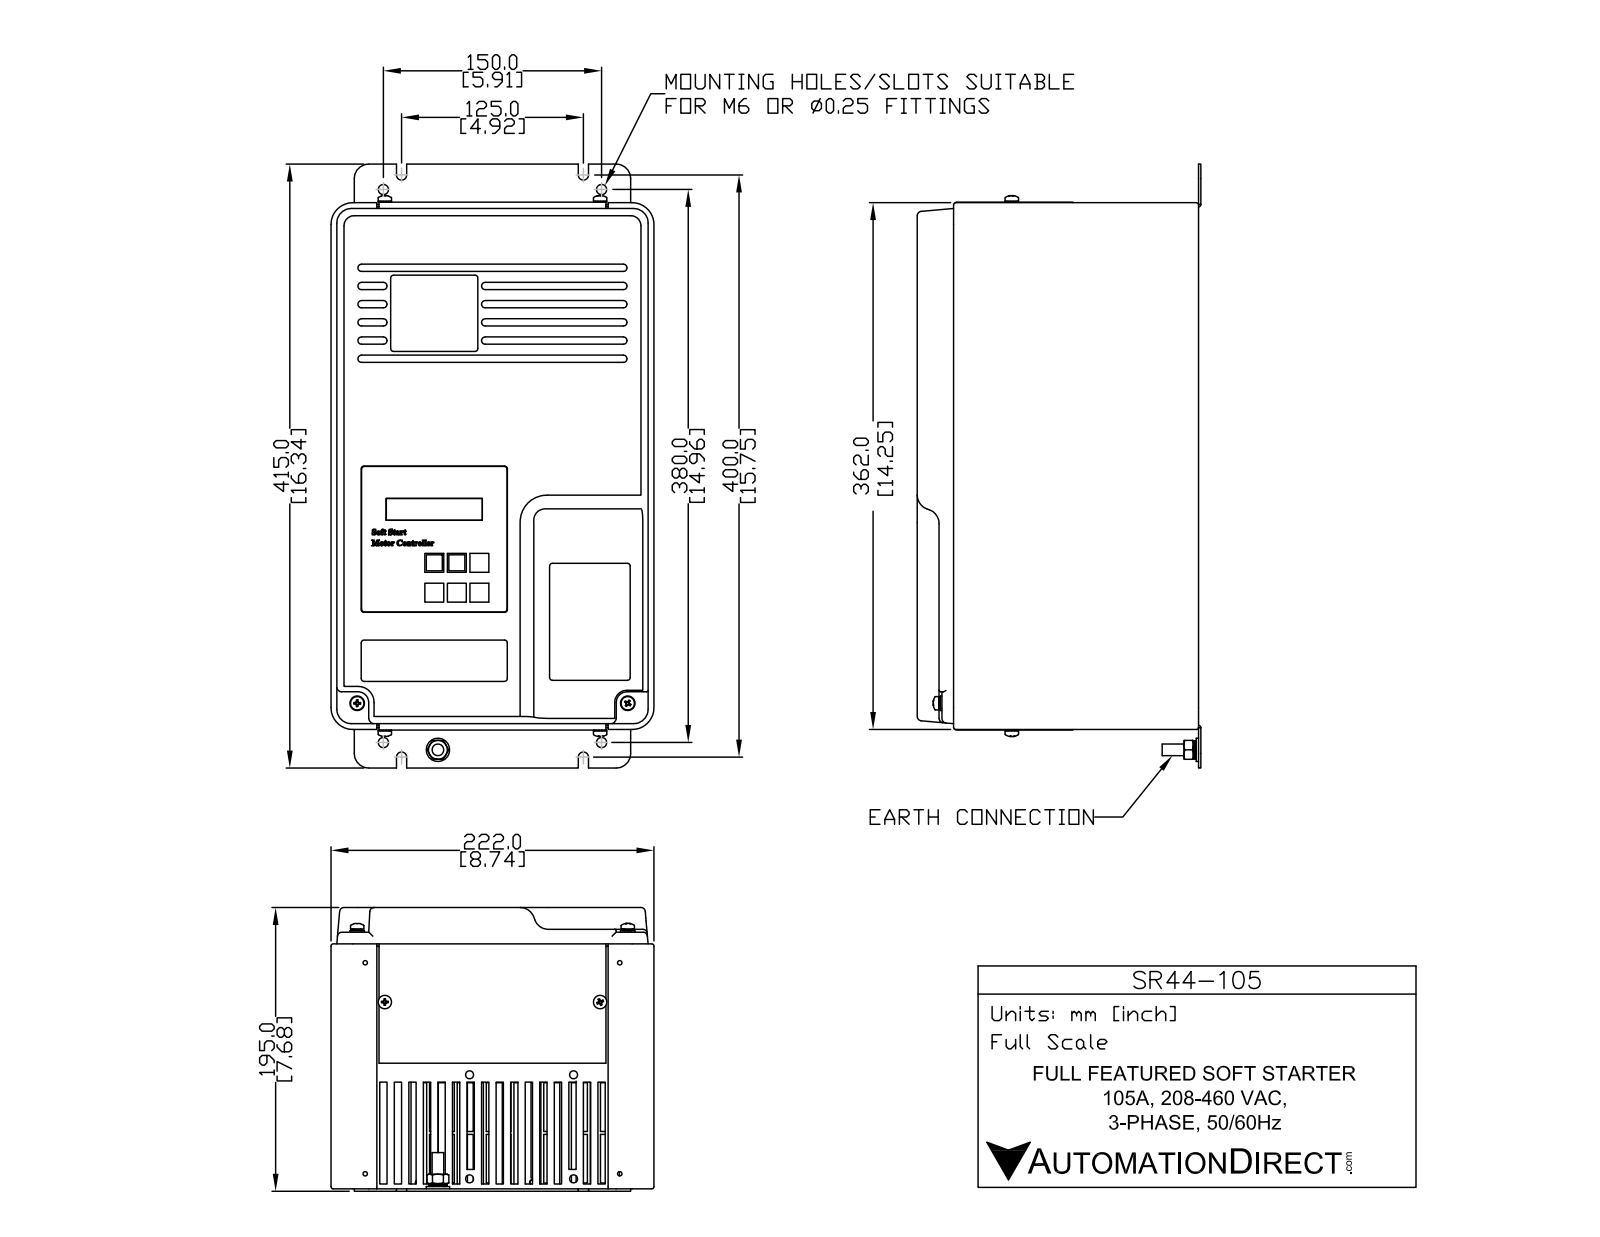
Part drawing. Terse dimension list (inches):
name: SR44-105
written by: SolidWorks 2013 (AUTOMOTIVE_DESIGN)
unit: in
bodies: 1 solid, 768 faces (455 planar, 175 cylindrical, 138 other)
size: 16.339 × 8.74 × 7.665
volume: 502.3 in³; area: 1 102 in²
holes: 4× ⌀0.276
bosses: 4× ⌀0.394, 1× ⌀0.63, 1× ⌀0.315
rounds: 30× R0.098, 28× R0.094, 12× R0.098, 11× R0.059, 8× R0.118, 8× R0.394, 6× R0.079, 4× R0.138
face distances: 0.401, 0.802, 1.204, 1.605, 2.006, 2.407, 2.808, 0.232, 3.209, 8.508
hole spacings: 5.906, 14.961, 16.084
